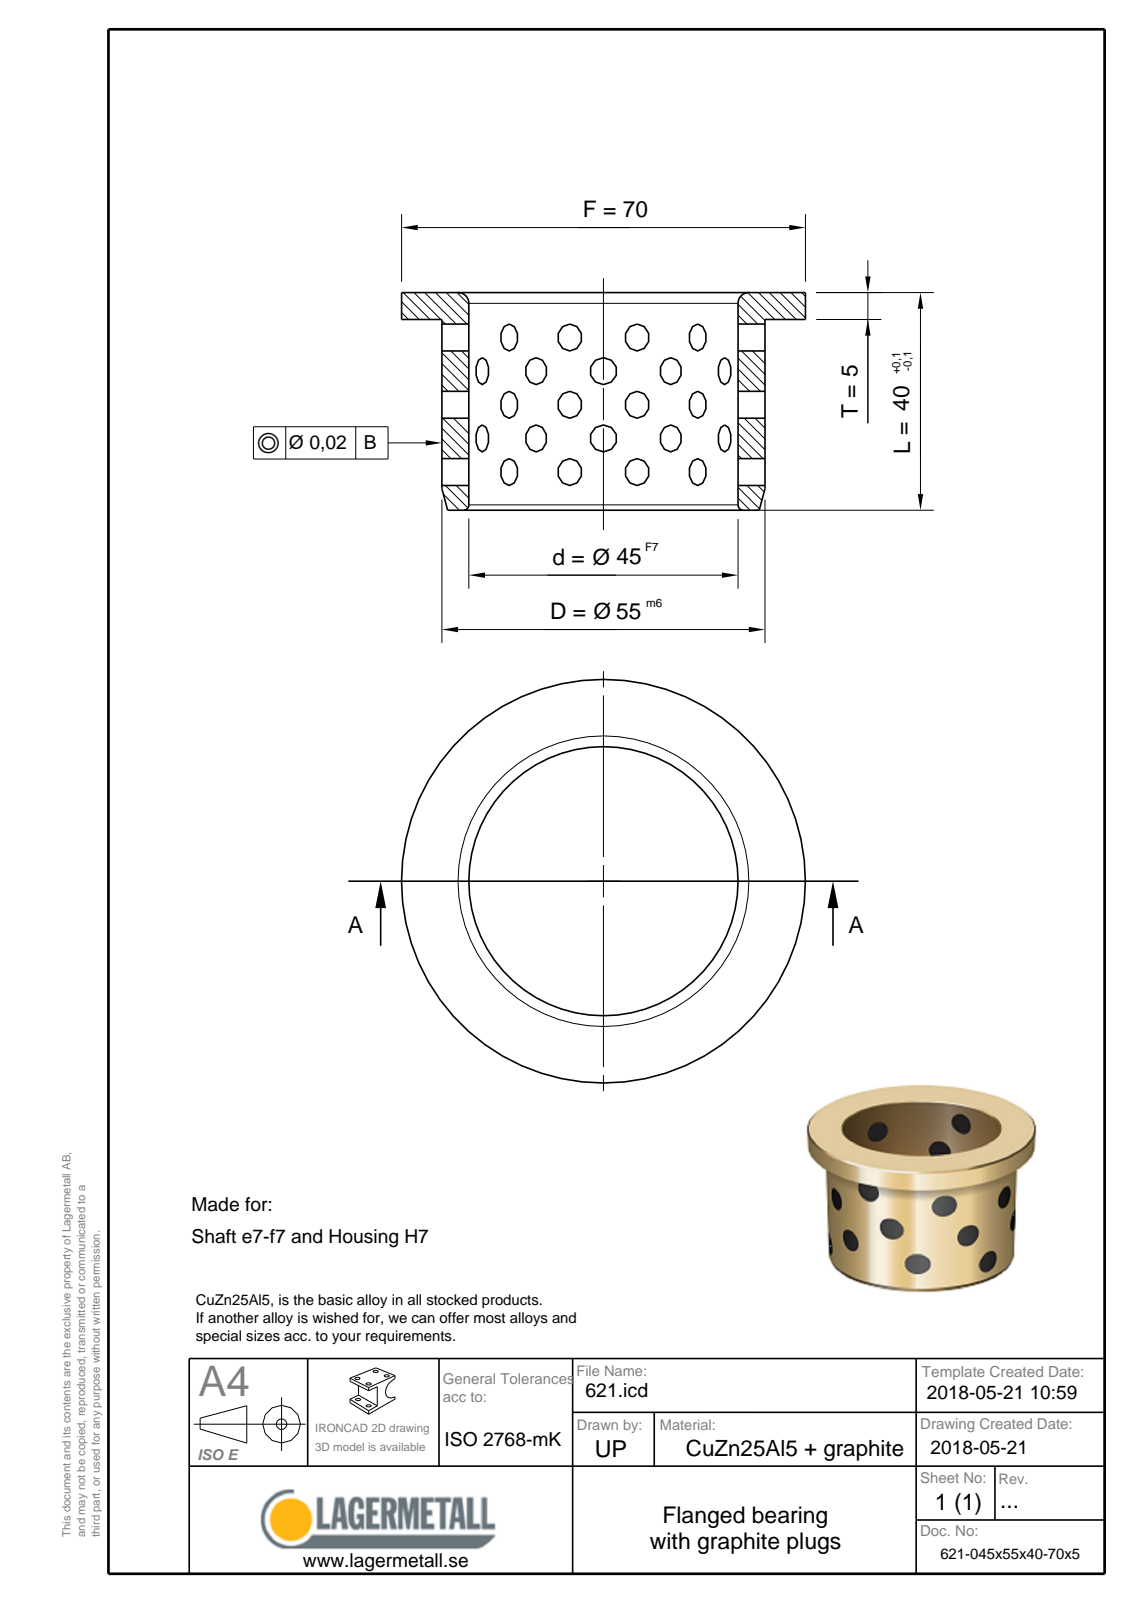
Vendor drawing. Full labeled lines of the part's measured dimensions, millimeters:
Part name (STEP PRODUCT): 621-045x55x40-70x5
STEP written by: Spatial InterOp 3D (CONFIG_CONTROL_DESIGN)
Units: millimetres
Bodies: 1 solid, 9 faces (3 planar, 3 cylindrical, 3 other)
Overall size (bounding box): 70 × 70 × 40
Volume: 38 327 mm³ · Surface area: 16 954 mm²
Round holes (diameter × count): ⌀45 ×1
Round bosses / shafts (diameter × count): ⌀70 ×1, ⌀55 ×1
Main face-to-face distances: 5, 35, 40
